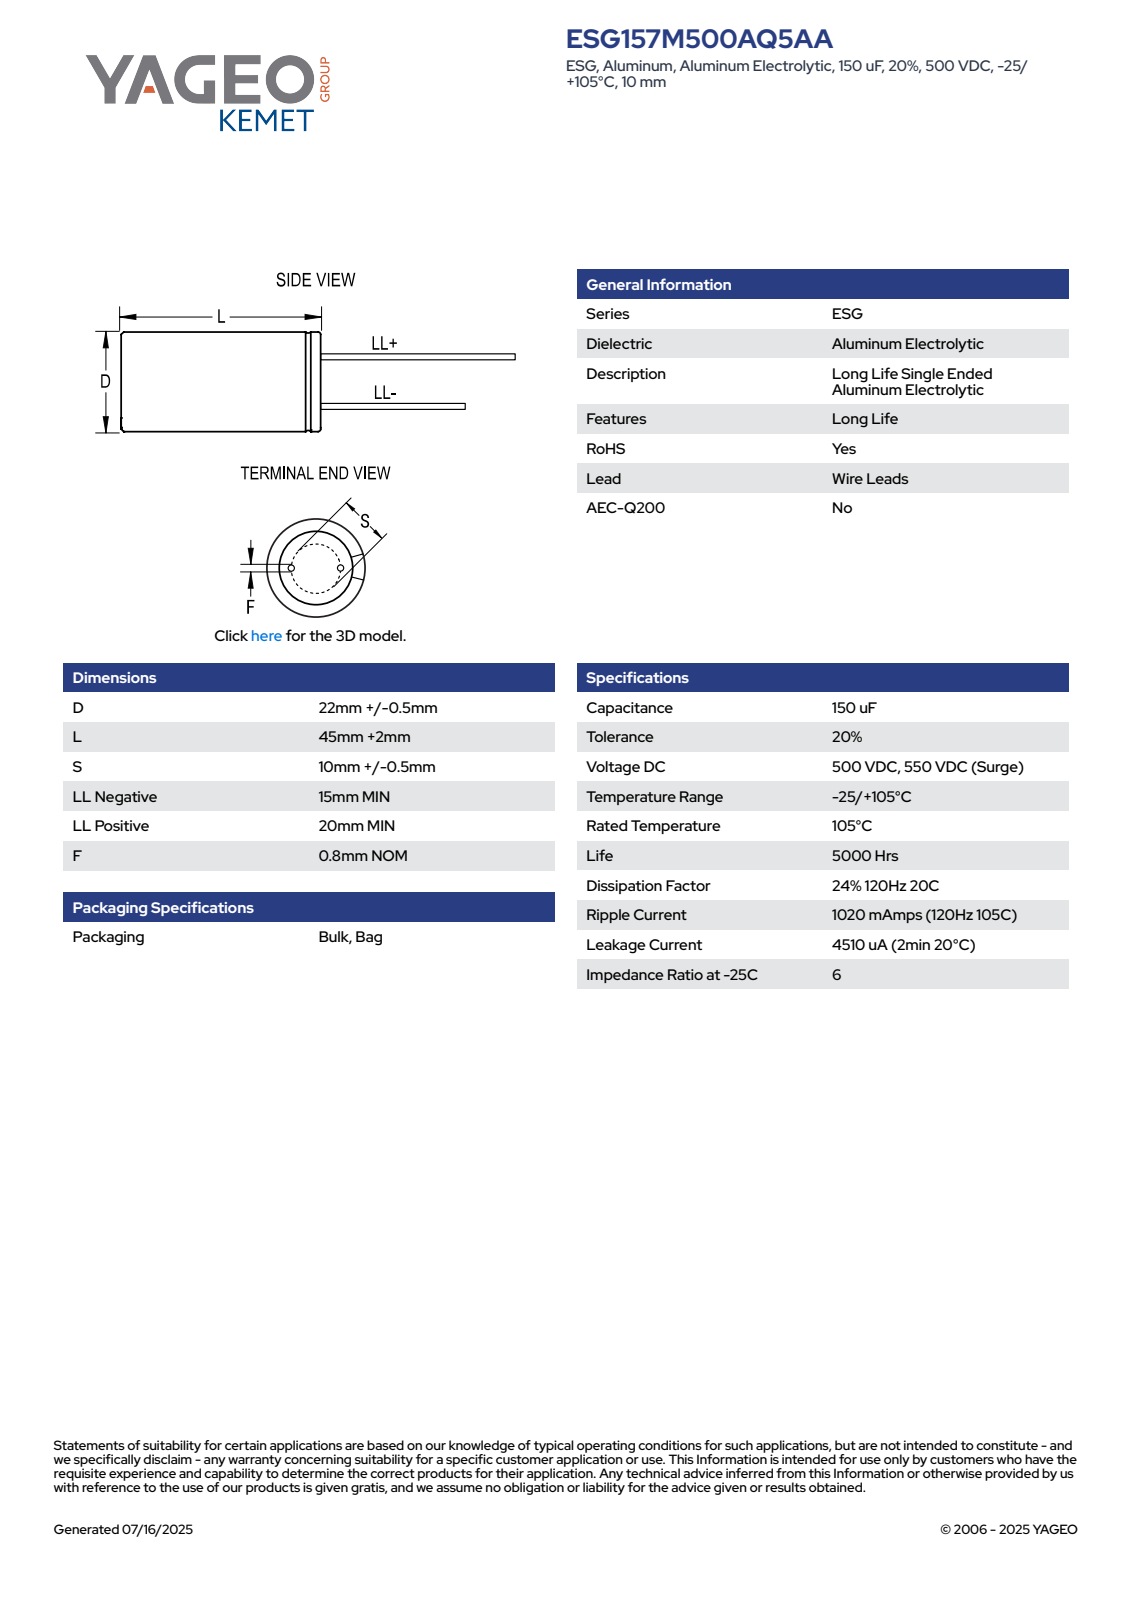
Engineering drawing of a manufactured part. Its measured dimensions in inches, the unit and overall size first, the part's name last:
Units: inches
Overall size (bounding box): 2.638 × 0.886 × 0.886
Round bosses / shafts (diameter × count): ⌀0.031 ×2, ⌀0.886 ×1
Main face-to-face distances: 1.85, 1.851, 2.441, 2.638, 2.441, 2.638, 0.591, 0.787, 0.197, 0.119
Volume: 1.134 in³ · Surface area: 6.704 in²
Bodies: 4 solids, 75 faces (61 planar, 8 cylindrical, 6 other)
Part name (STEP PRODUCT): CAR_KLP_22X45_D22.5L47S10F0.8
STEP written by: SolidWorks 2014 (AUTOMOTIVE_DESIGN)
